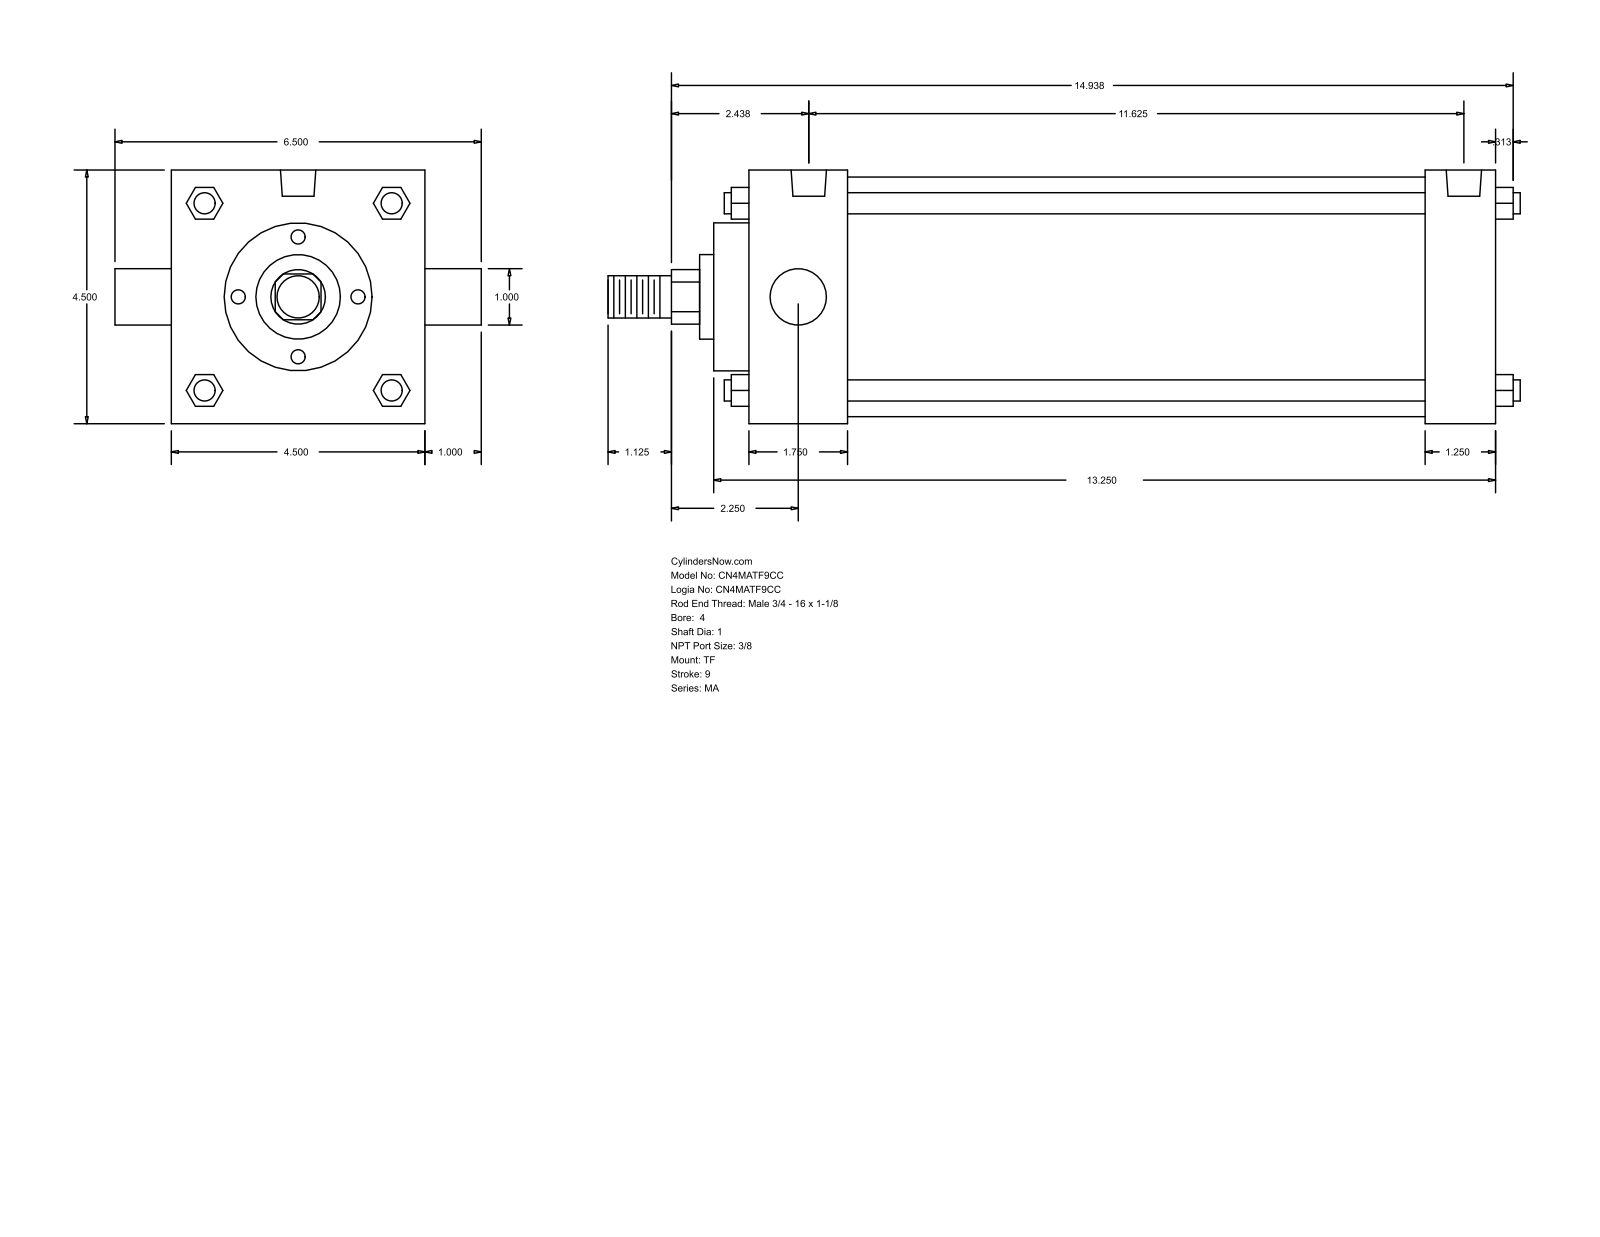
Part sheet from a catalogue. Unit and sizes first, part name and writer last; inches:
Units: inches
Overall size (bounding box): 16.187 × 6.5 × 4.5
Round holes (diameter × count): ⌀0.437 ×3, ⌀0.627 ×2
Round bosses / shafts (diameter × count): ⌀0.375 ×4, ⌀1 ×2, ⌀4.25 ×1, ⌀2.625 ×1, ⌀1.5 ×1, ⌀0.75 ×1
Partial cylindrical surfaces — rounded edges, fillets, slot ends (radius × count): R0.484 ×1
Main face-to-face distances: 4.5, 13.25, 12, 1.25, 1.75, 10.25, 11.5, 0.625, 2.375, 12.625
Hole centre spacings: 0.187, 11.438, 11.25, 11.625
Bodies: 0 solids, 122 faces (93 planar, 29 cylindrical, 0 other)
Part name (STEP PRODUCT): MA_TF__0400_1
STEP written by: GSSL Pune (CONFIG_CONTROL_DESIGN)
